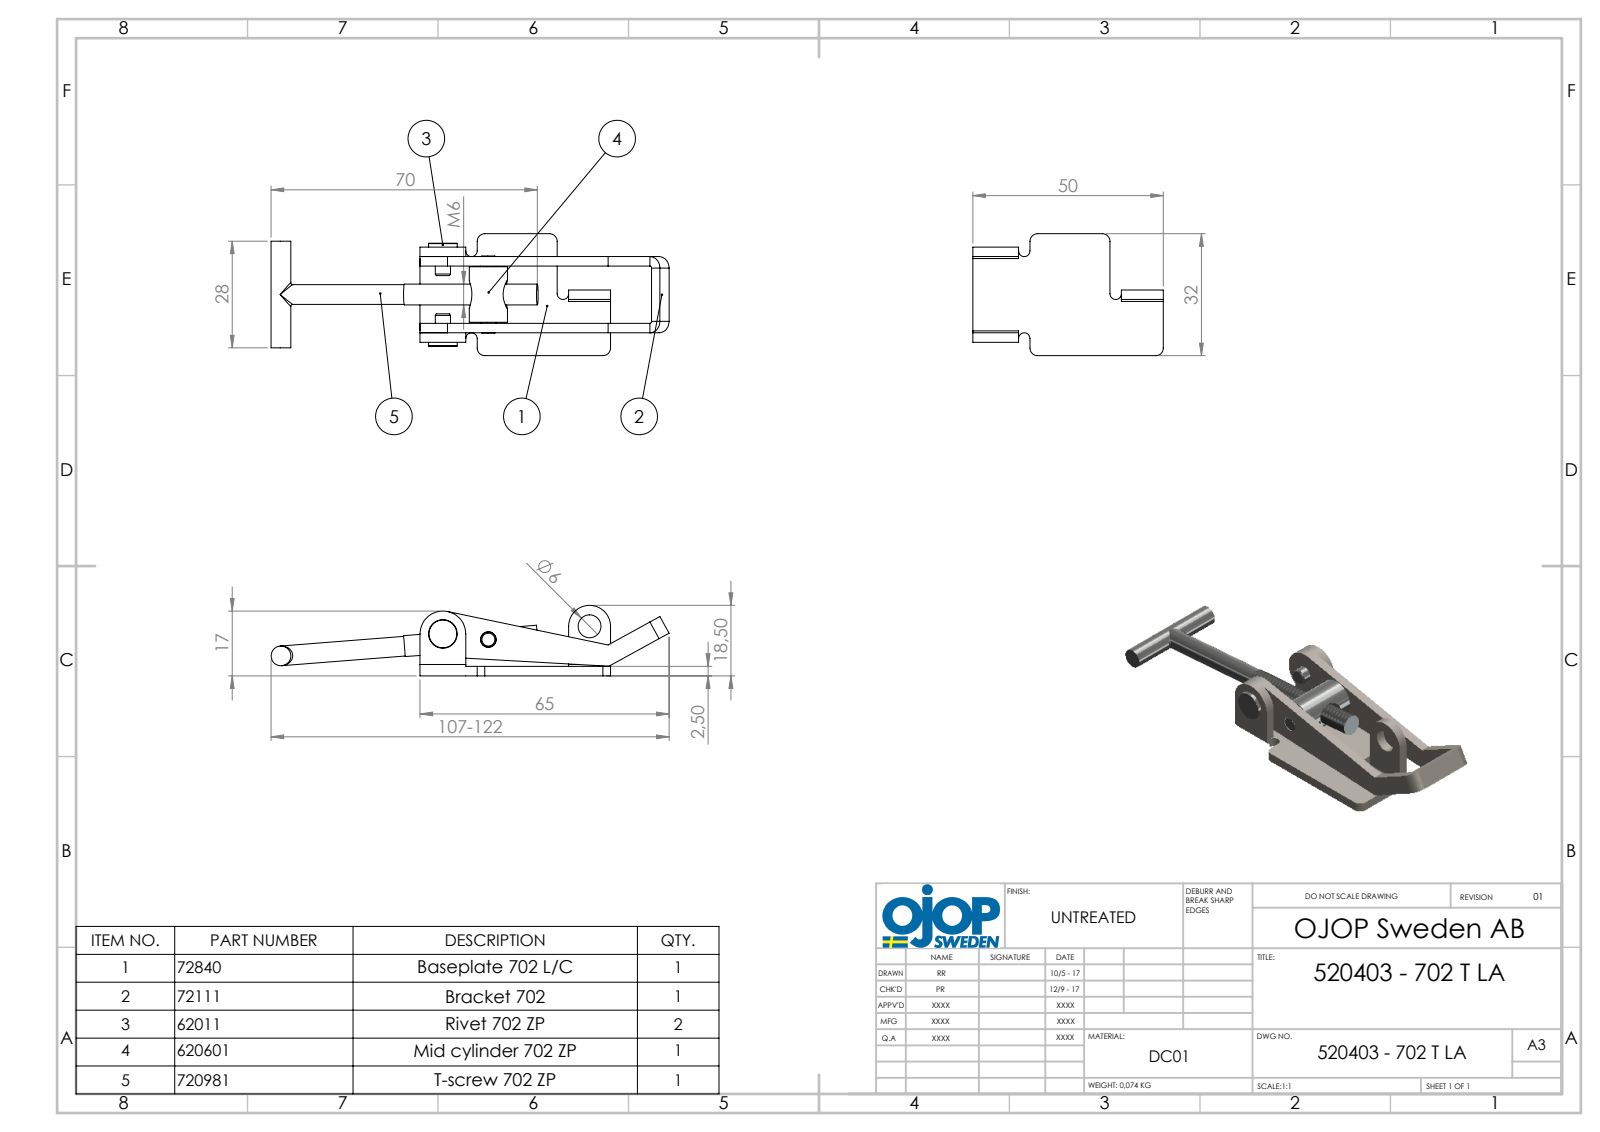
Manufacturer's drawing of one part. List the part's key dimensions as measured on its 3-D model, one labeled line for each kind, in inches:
Part name (STEP PRODUCT): 702 - Rulle; 702 - Ansatsnit; 520403 - 702 T LA; 702 - Bygel (+2 more)
STEP written by: SolidWorks 2015 (AUTOMOTIVE_DESIGN)
Units: inches
Bodies: 6 solids, 149 faces (66 planar, 65 cylindrical, 18 other)
Overall size (bounding box): 4.217 × 1.26 × 0.728
Volume: 0.631 in³ · Surface area: 15.38 in²
Round holes (diameter × count): ⌀0.161 ×2, ⌀0.236 ×2, ⌀0.197 ×1
Round bosses / shafts (diameter × count): ⌀0.208 ×2, ⌀0.157 ×2, ⌀0.394 ×1, ⌀0.295 ×1, ⌀0.236 ×1
Partial cylindrical surfaces — rounded edges, fillets, slot ends (radius × count): R0.02 ×5, R0.118 ×5, R0.079 ×4, R0.059 ×2, R0.059 ×1, R0.217 ×1, R0.236 ×1
Main face-to-face distances: 0.098, 0.689, 0.787, 0.344, 0.443, 0.591, 0.197, 0.246, 0.886, 0.236
Hole centre spacings: 0.473, 1.055, 1.518
